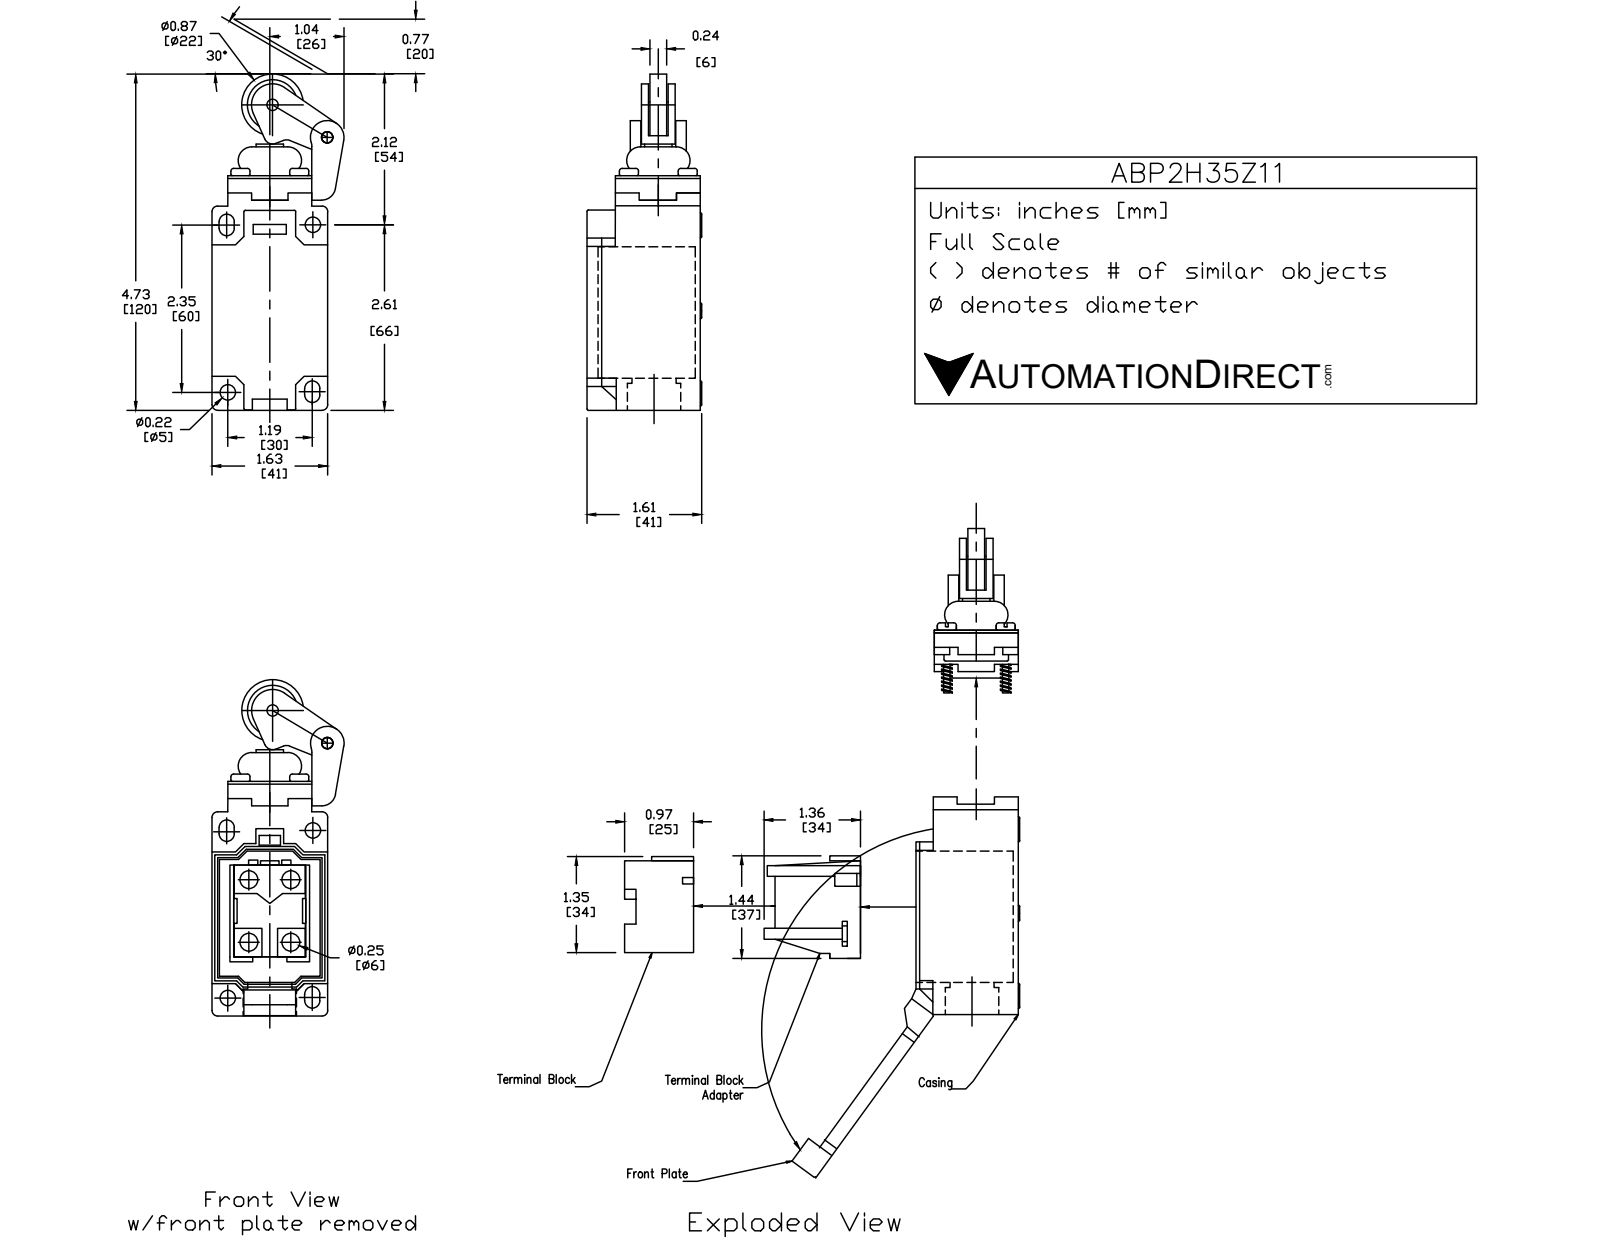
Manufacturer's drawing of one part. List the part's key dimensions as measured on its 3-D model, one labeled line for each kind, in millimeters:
Part name (STEP PRODUCT): ABP2H35Z11
STEP written by: SolidWorks 2017 (AUTOMOTIVE_DESIGN)
Units: millimetres
Bodies: 4 solids, 241 faces (111 planar, 104 cylindrical, 26 other)
Overall size (bounding box): 119.3 × 47.5 × 40.3
Volume: 129 100 mm³ · Surface area: 28 320 mm²
Round holes (diameter × count): ⌀5.4 ×2, ⌀10.1 ×1, ⌀17 ×1, ⌀19 ×1, ⌀20.5 ×1
Round bosses / shafts (diameter × count): ⌀7 ×5, ⌀9 ×4, ⌀10 ×2, ⌀22 ×1, ⌀13 ×1, ⌀5.8 ×1
Partial cylindrical surfaces — rounded edges, fillets, slot ends (radius × count): R0.5 ×12, R2 ×8, R0.6 ×4, R2.7 ×4, R12 ×2, R3 ×1, R5 ×1, R7.5 ×1
Main face-to-face distances: 41, 39.8, 30, 12, 75.5, 8.3, 3, 18.7, 9.8, 4
Hole centre spacings: 1.5, 67.1
